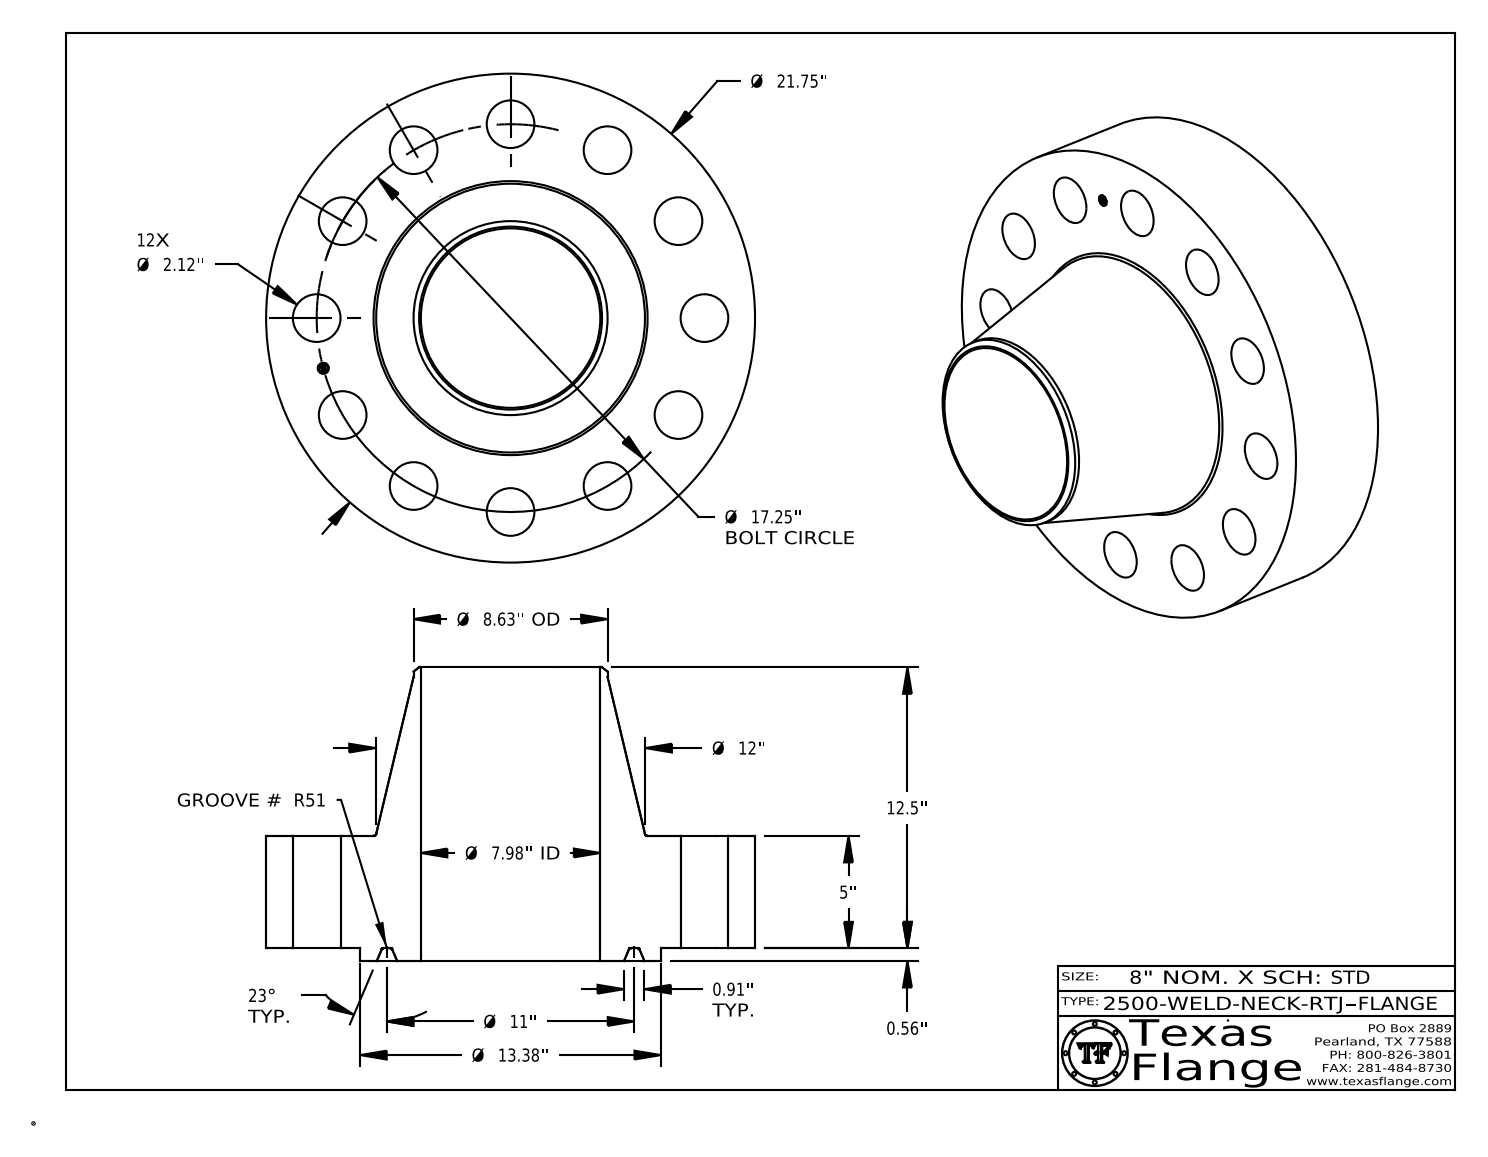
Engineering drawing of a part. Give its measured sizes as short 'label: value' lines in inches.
name: 2500-WELD-NECK-RTJ
written by: CATIA V5 STEP AP214 (AUTOMOTIVE_DESIGN)
unit: in
bodies: 1 solid, 437 faces (371 planar, 52 cylindrical, 14 other)
size: 21.75 × 21.75 × 13.063
volume: 1 679 in³; area: 1 864 in²
holes: 12× ⌀2.12, 1× ⌀0.495, 1× ⌀7.981
bosses: 8× ⌀0.03, 1× ⌀21.75, 1× ⌀13.375, 1× ⌀8.63, 1× ⌀0.39
face distances: 5, 0.563, 5.563, 13.063, 12.5, 7.5, 5.548, 4.985, 0.015, 7.515
hole spacings: 8.625, 16.662, 4.465, 8.625, 12.198, 14.939, 4.464, 12.198
